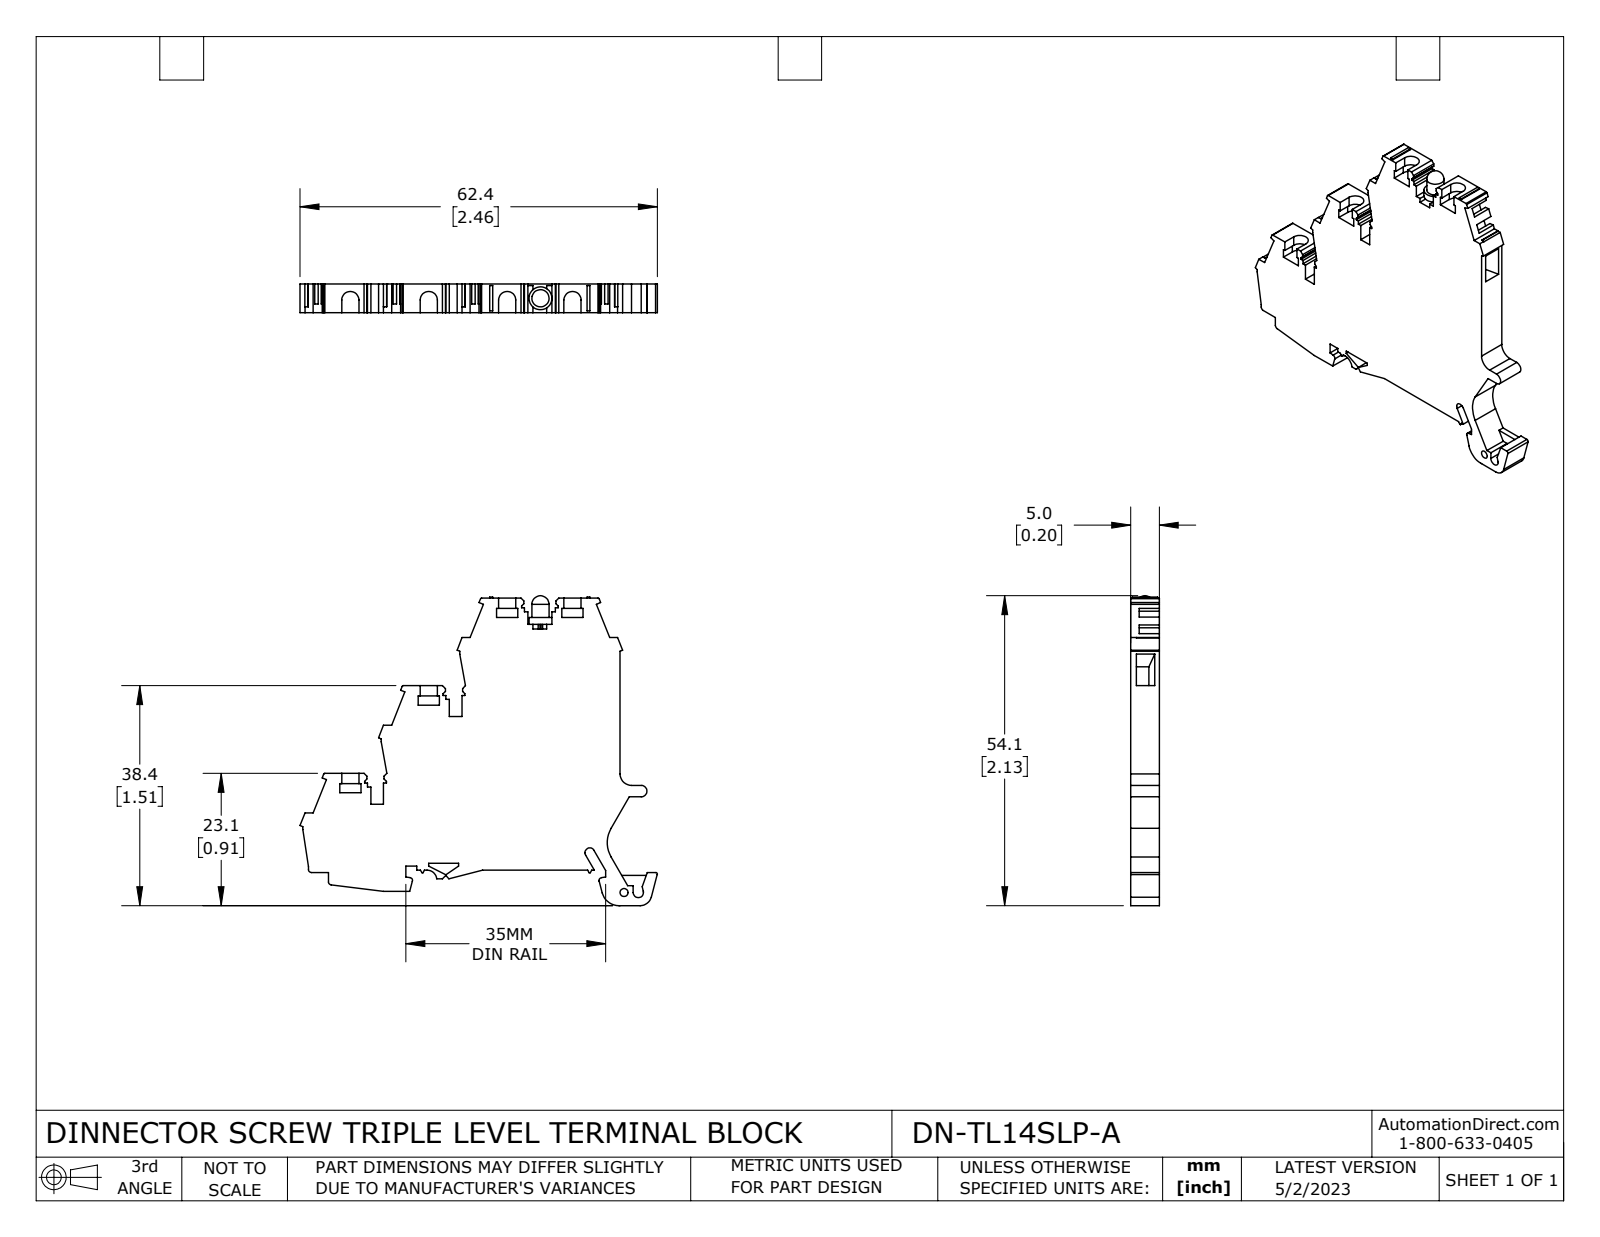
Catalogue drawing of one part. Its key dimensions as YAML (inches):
part_name: "20621; 43505_DN-TL14S-A; DN-TL14SLP-A"
step_written_by: "SolidWorks 2017 (AUTOMOTIVE_DESIGN)"
units: inches
bodies: {solids: 2, faces: 383, planar: 299, cylindrical: 67, other: 17}
overall_size: [2.456, 2.128, 0.197]
volume: 0.555
surface_area: 9.684
round_holes:
  - {diameter: 0.102, count: 4}
  - {diameter: 0.055, count: 1}
round_bosses_or_shafts:
  - {diameter: 0.012, count: 10}
  - {diameter: 0.157, count: 1}
  - {diameter: 0.118, count: 1}
partial_cylinders:
  - {radius: 0.02, count: 8}
  - {radius: 0.008, count: 4}
  - {radius: 0.059, count: 4}
  - {radius: 0.073, count: 4}
  - {radius: 0.079, count: 2}
  - {radius: 0.012, count: 1}
  - {radius: 0.033, count: 1}
  - {radius: 0.035, count: 1}
face_to_face_distances: [0.197, 0.602, 0.039, 0.157, 0.087, 0.079, 0.278, 0.469, 0.539, 1.205]
hole_center_spacings: [0.809, 0.874, 1.536, 1.617, 1.667, 1.881, 1.947, 2.144]
